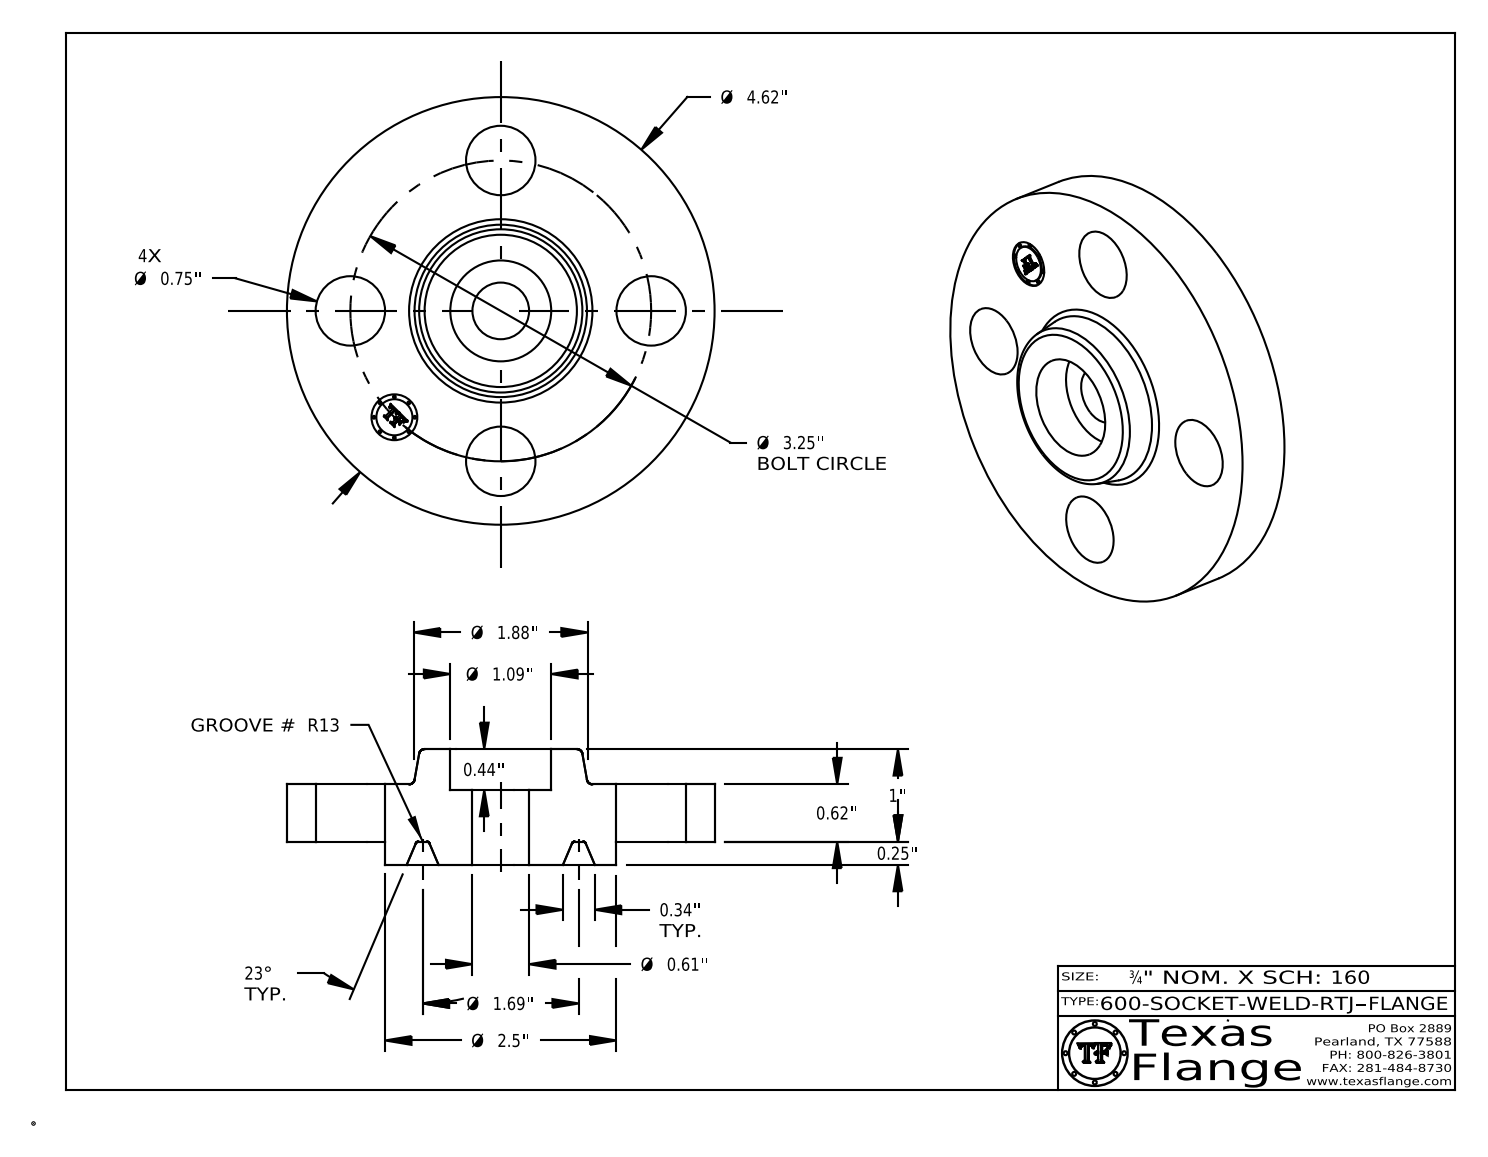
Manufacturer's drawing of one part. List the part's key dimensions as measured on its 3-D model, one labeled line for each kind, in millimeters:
Part name (STEP PRODUCT): 600-SOCKET-WELD-RTJ
STEP written by: CATIA V5 STEP AP214 (AUTOMOTIVE_DESIGN)
Units: millimetres
Bodies: 1 solid, 422 faces (372 planar, 36 cylindrical, 14 other)
Overall size (bounding box): 117.3 × 117.3 × 31.8
Volume: 172 700 mm³ · Surface area: 34 000 mm²
Round holes (diameter × count): ⌀19.1 ×4, ⌀12.6 ×1, ⌀15.5 ×1, ⌀27.7 ×1
Round bosses / shafts (diameter × count): ⌀0.8 ×8, ⌀117.3 ×1, ⌀63.5 ×1, ⌀9.9 ×1
Main face-to-face distances: 15.7, 6.4, 22.1, 31.8, 25.4, 9.7, 20.6, 14.2, 1.5, 11.2
Hole centre spacings: 41.3, 58.4, 31.6, 76.3, 82.6
